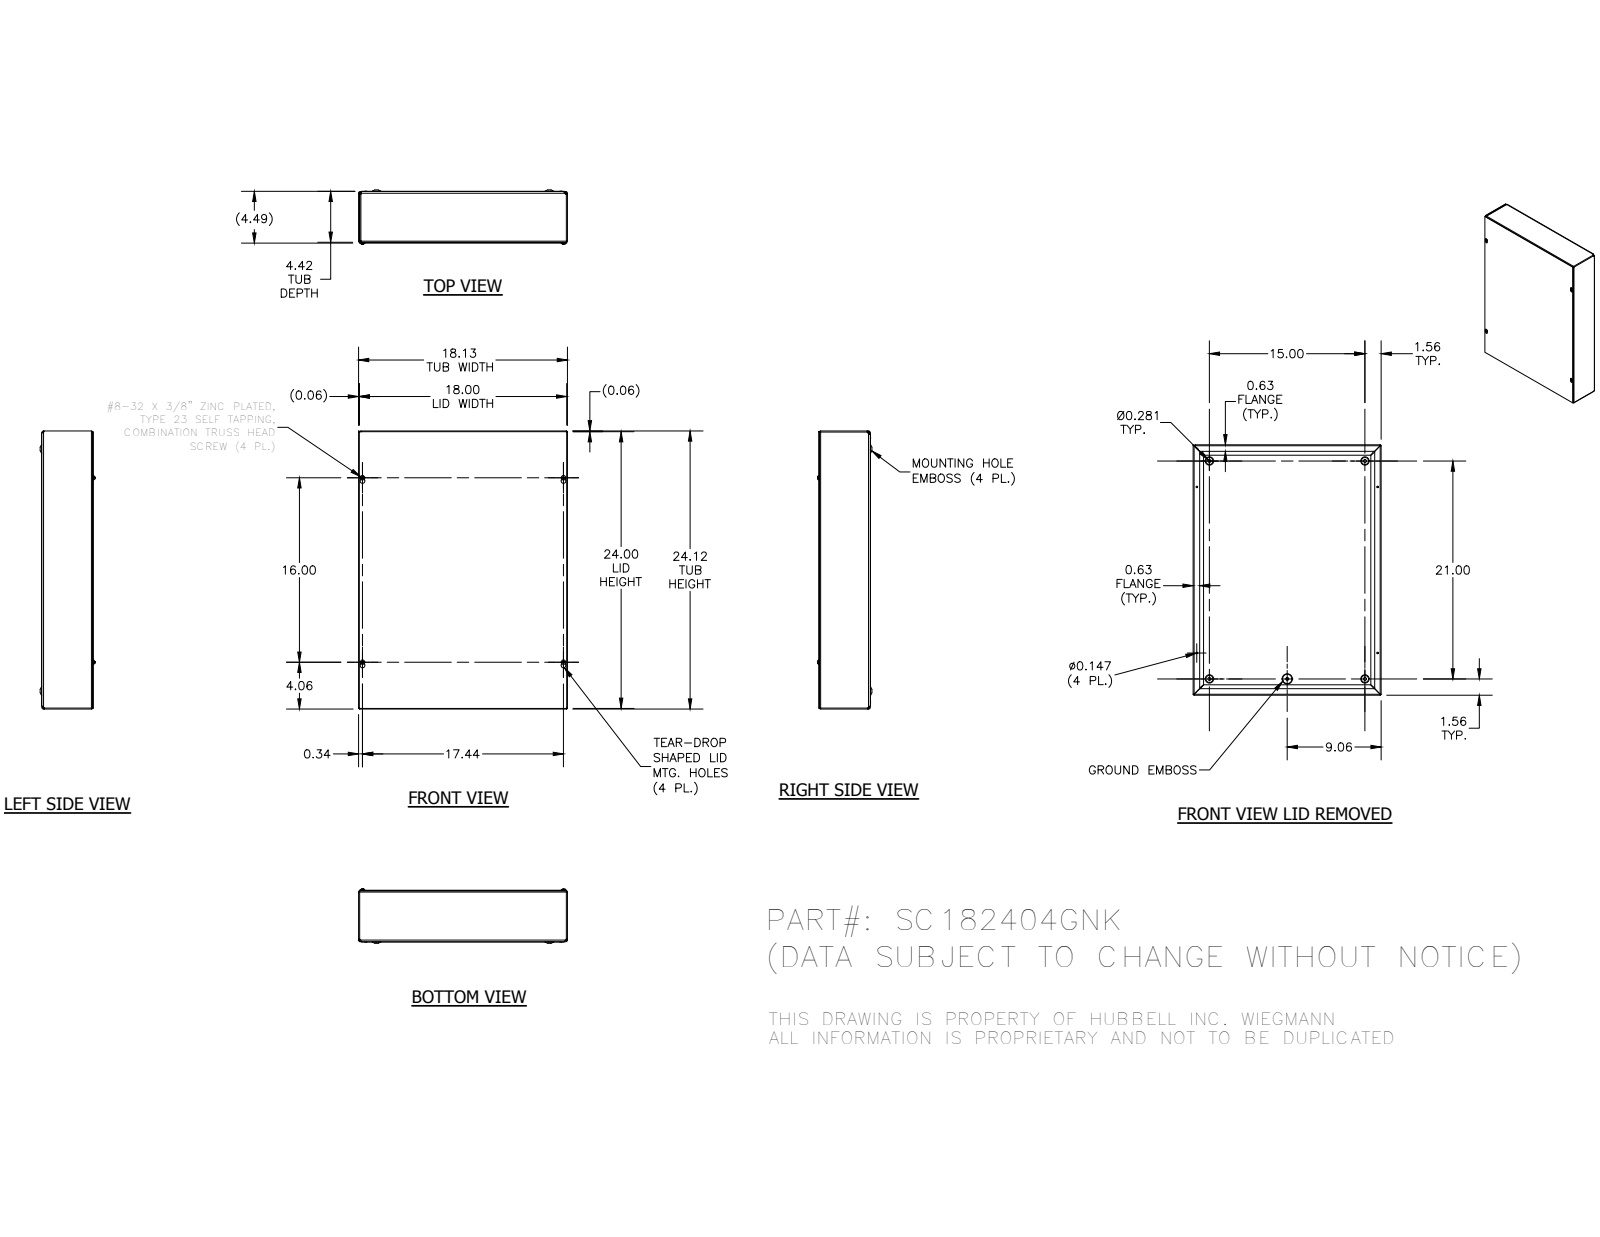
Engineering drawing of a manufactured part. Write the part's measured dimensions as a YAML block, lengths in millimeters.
part_name: "SC1824GNKBKP; SC182404GNKWRA; SC1824GNKLID; 34056 (+1 more)"
step_written_by: "Autodesk Inventor 2014 (AUTOMOTIVE_DESIGN)"
units: millimeters
bodies: {solids: 7, faces: 359, planar: 134, cylindrical: 81, other: 144}
overall_size: [612.77, 460.38, 119.79]
volume: 1526000
surface_area: 1743000
round_holes:
  - {diameter: 3.73, count: 4}
  - {diameter: 7.62, count: 4}
  - {diameter: 4.19, count: 1}
round_bosses_or_shafts:
  - {diameter: 4.57, count: 8}
  - {diameter: 9.75, count: 4}
  - {diameter: 4.17, count: 4}
  - {diameter: 5.8, count: 1}
partial_cylinders:
  - {radius: 0.79, count: 8}
  - {radius: 2.37, count: 8}
  - {radius: 1.4, count: 4}
  - {radius: 1.57, count: 4}
  - {radius: 2.38, count: 4}
  - {radius: 2.97, count: 4}
  - {radius: 3.15, count: 4}
  - {radius: 3.17, count: 4}
face_to_face_distances: [1.88, 112.2, 110.32, 114.08, 1.57, 611.2, 1.58, 460.38, 458.81, 458.8]
hole_center_spacings: [70.66, 190.5, 381, 406.4, 416.82, 442.91, 470.9, 470.94]
